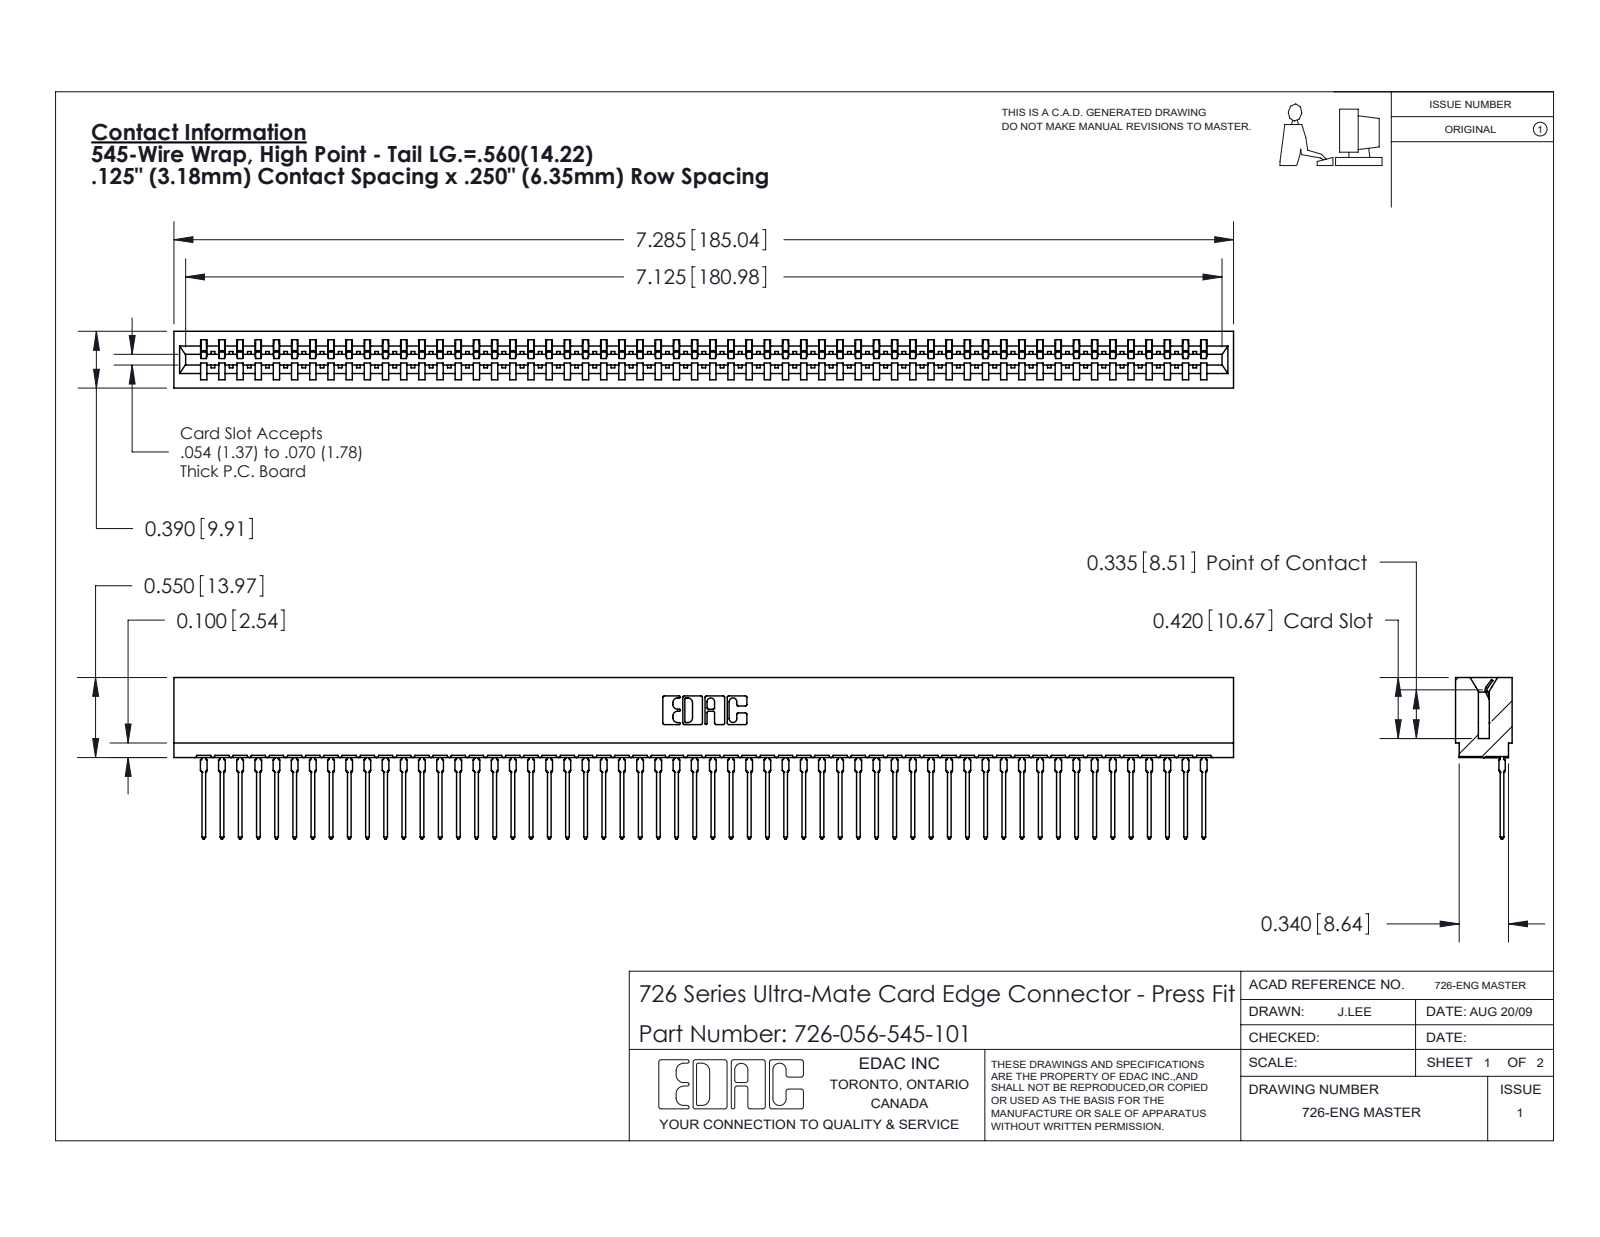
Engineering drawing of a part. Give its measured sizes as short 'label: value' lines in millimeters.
name: 726 Part_.515 Slot Depth - 01; 746-292-001_545; 726-056-545-101
written by: SolidWorks 2020 (CONFIG_CONTROL_DESIGN)
unit: mm
bodies: 57 solids, 6145 faces (3583 planar, 1106 cylindrical, 1456 other)
size: 185 × 28.2 × 9.9
volume: 16 600 mm³; area: 26 320 mm²
rounds: 112× R0.5, 57× R0.4, 22× R0.3, 6× R0.2, 6× R0.8, 4× R0.1, 4× R0.3, 3× R0.7
face distances: 1.4, 8.5, 9.9, 0.6, 7.8, 6.4, 2.1, 7, 9.3, 0.8
